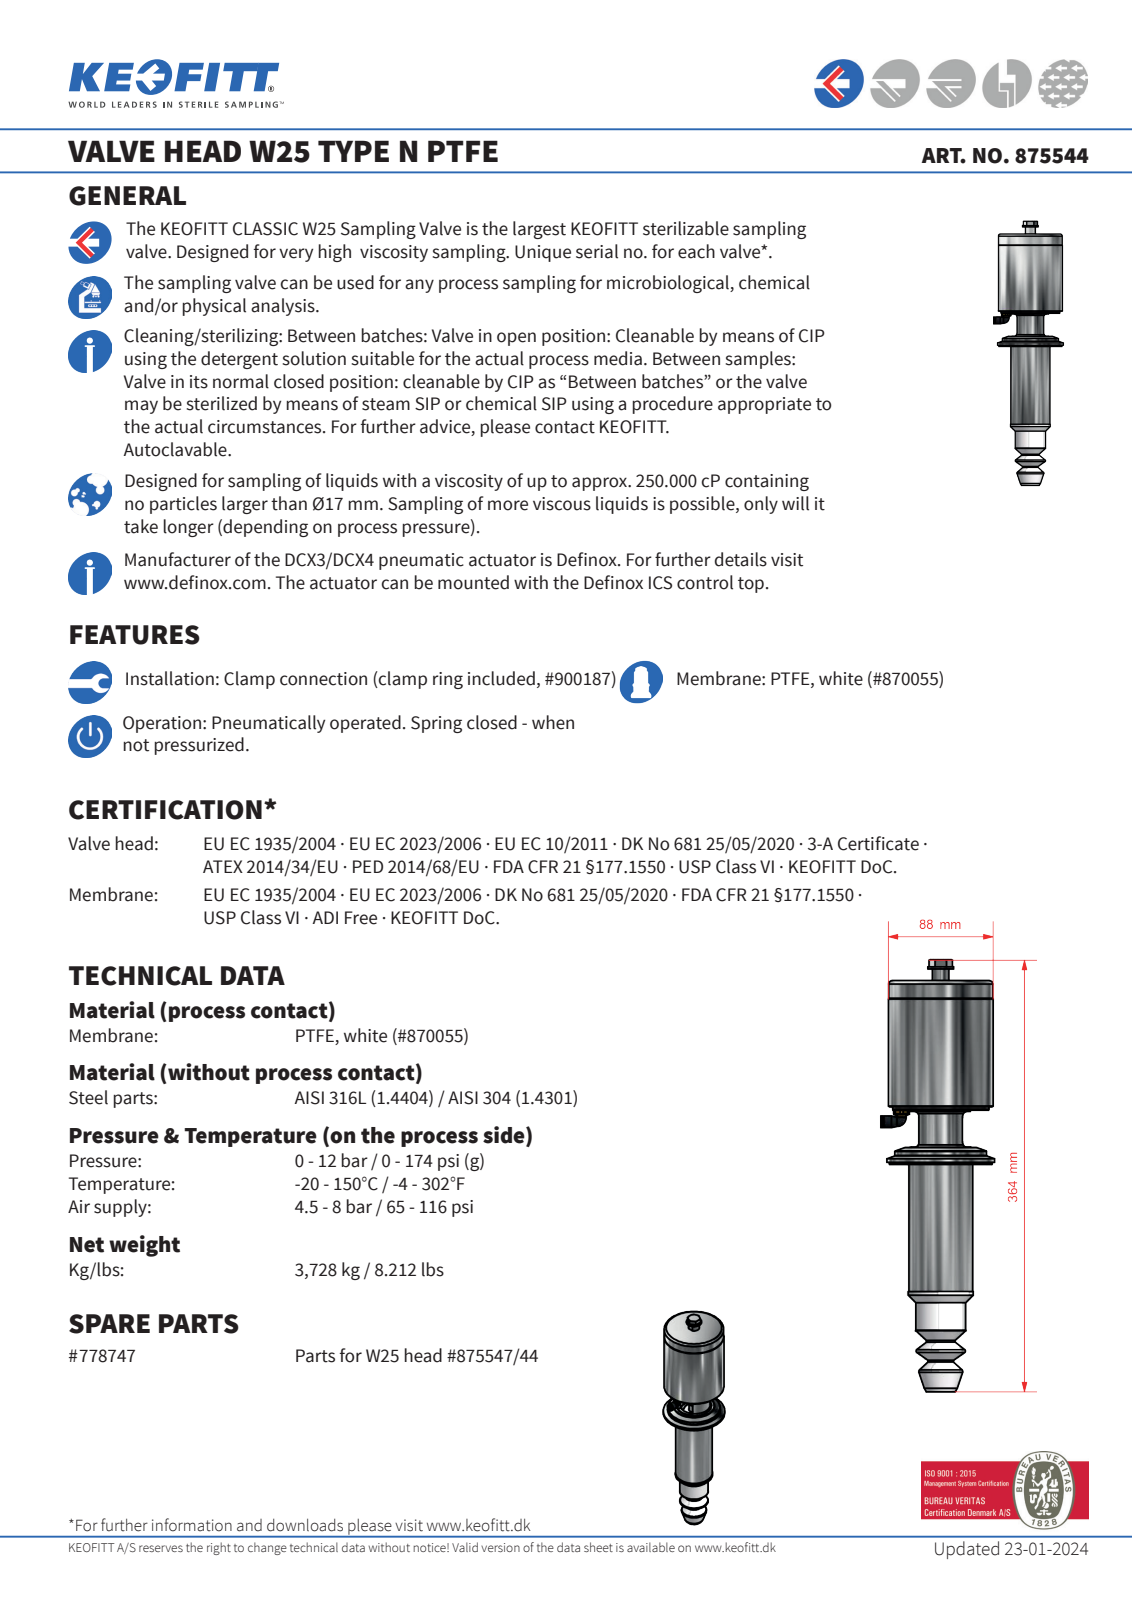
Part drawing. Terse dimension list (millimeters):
name: 875544_Simplify_1
written by: Autodesk Inventor 2022 (AUTOMOTIVE_DESIGN)
unit: mm
bodies: 5 solids, 363 faces (98 planar, 129 cylindrical, 136 other)
size: 364.4 × 138.68 × 114.42
volume: 1 177 000 mm³; area: 136 688 mm²
holes: 1× ⌀40.05, 1× ⌀50
bosses: 3× ⌀4, 2× ⌀8, 2× ⌀7.8, 1× ⌀91, 1× ⌀88.35, 1× ⌀88, 1× ⌀87, 1× ⌀81.2
rounds: 36× R1, 22× R2, 8× R5, 4× R4, 2× R0.4, 2× R5.1, 2× R5.95, 2× R45.5
face distances: 155.23, 45.8, 109.43, 107.04, 152.84, 262.27, 107.6, 0.56, 45.24, 154.67
